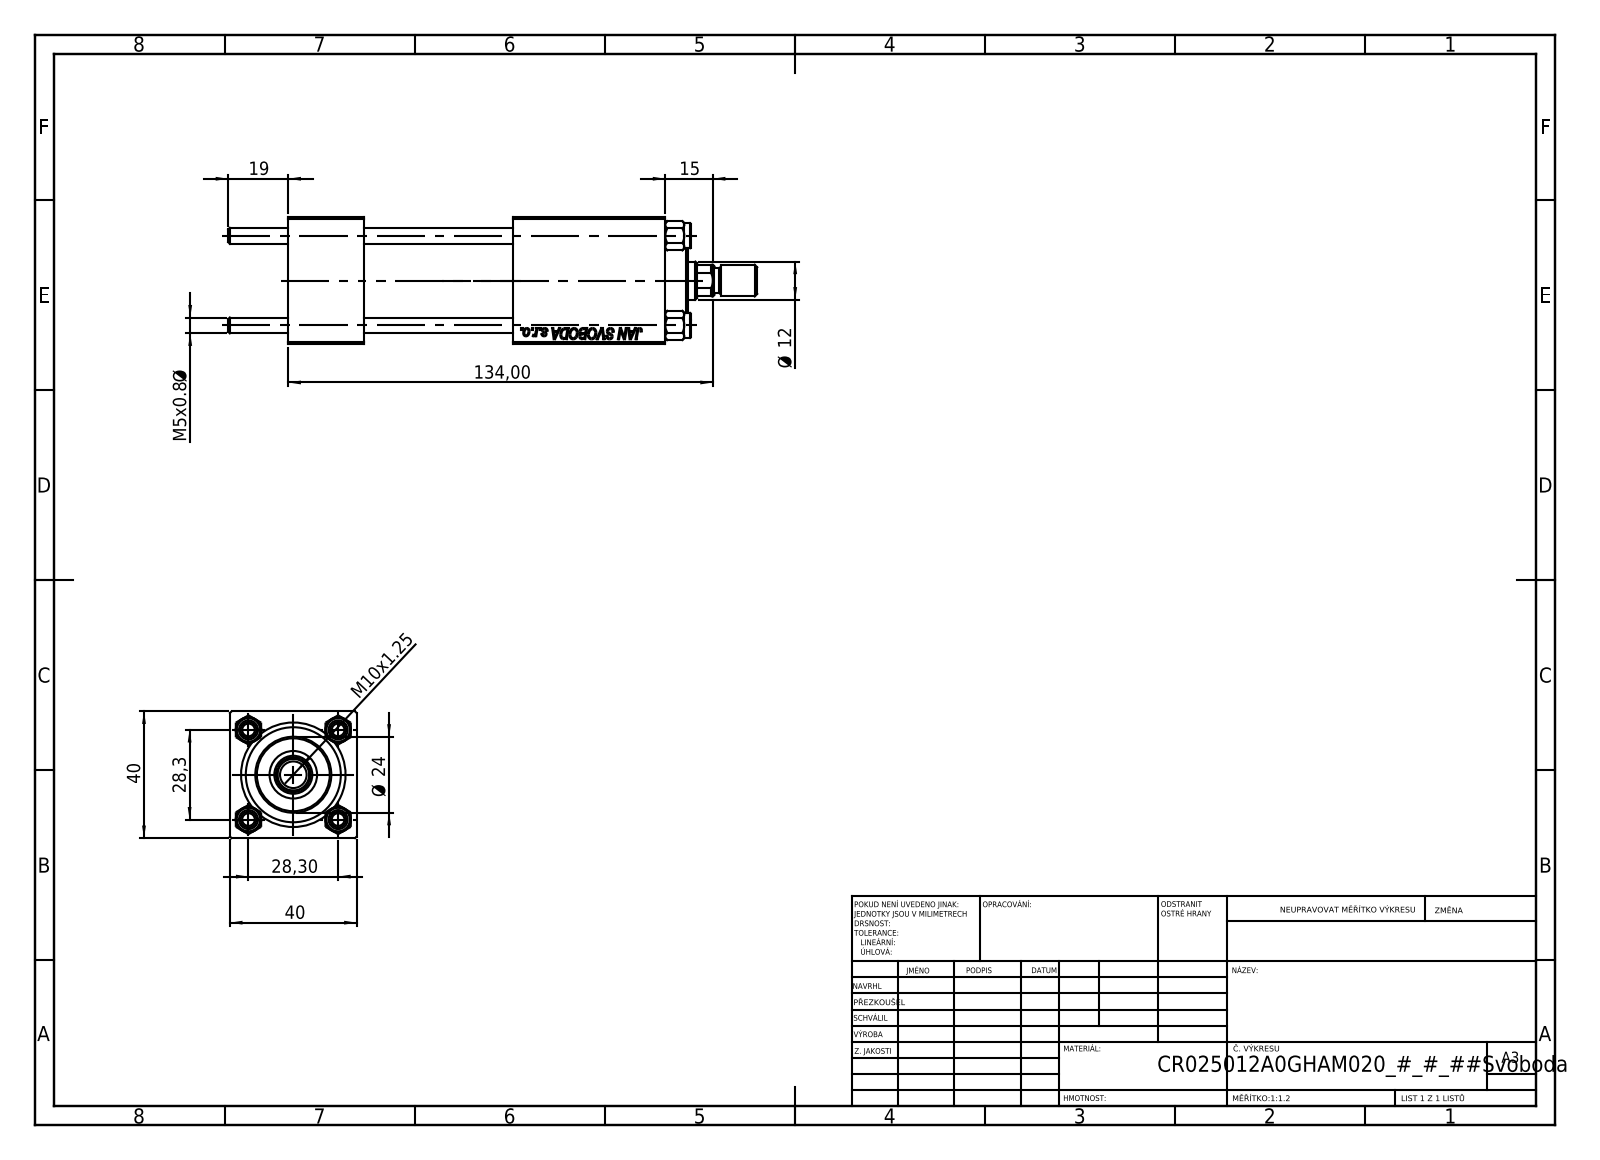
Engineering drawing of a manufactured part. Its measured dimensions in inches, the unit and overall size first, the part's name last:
Units: inches
Overall size (bounding box): 6.575 × 1.575 × 1.575
Round holes (diameter × count): ⌀0.197 ×4, ⌀0.787 ×3, ⌀0.276 ×2, ⌀0.518 ×2, ⌀0.256 ×1, ⌀0.472 ×1, ⌀0.591 ×1, ⌀0.984 ×1, ⌀1.181 ×1
Round bosses / shafts (diameter × count): ⌀0.315 ×5, ⌀1.22 ×1, ⌀0.945 ×1, ⌀0.394 ×1
Partial cylindrical surfaces — rounded edges, fillets, slot ends (radius × count): R0.217 ×1
Main face-to-face distances: 1.575, 0.945, 4.685, 3.74, 3.555, 2.61, 1.13, 2.795, 1.85, 0.76
Hole centre spacings: 0.788, 1.114, 1.576, 2.835
Volume: 8.901 in³ · Surface area: 92.2 in²
Bodies: 12 solids, 1145 faces (521 planar, 82 cylindrical, 542 other)
Part name (STEP PRODUCT): V215_VC_A; NUT_M5; V215CR_VCP; ROD_END_AH (+2 more)
STEP written by: SolidWorks 2019 (CONFIG_CONTROL_DESIGN)
